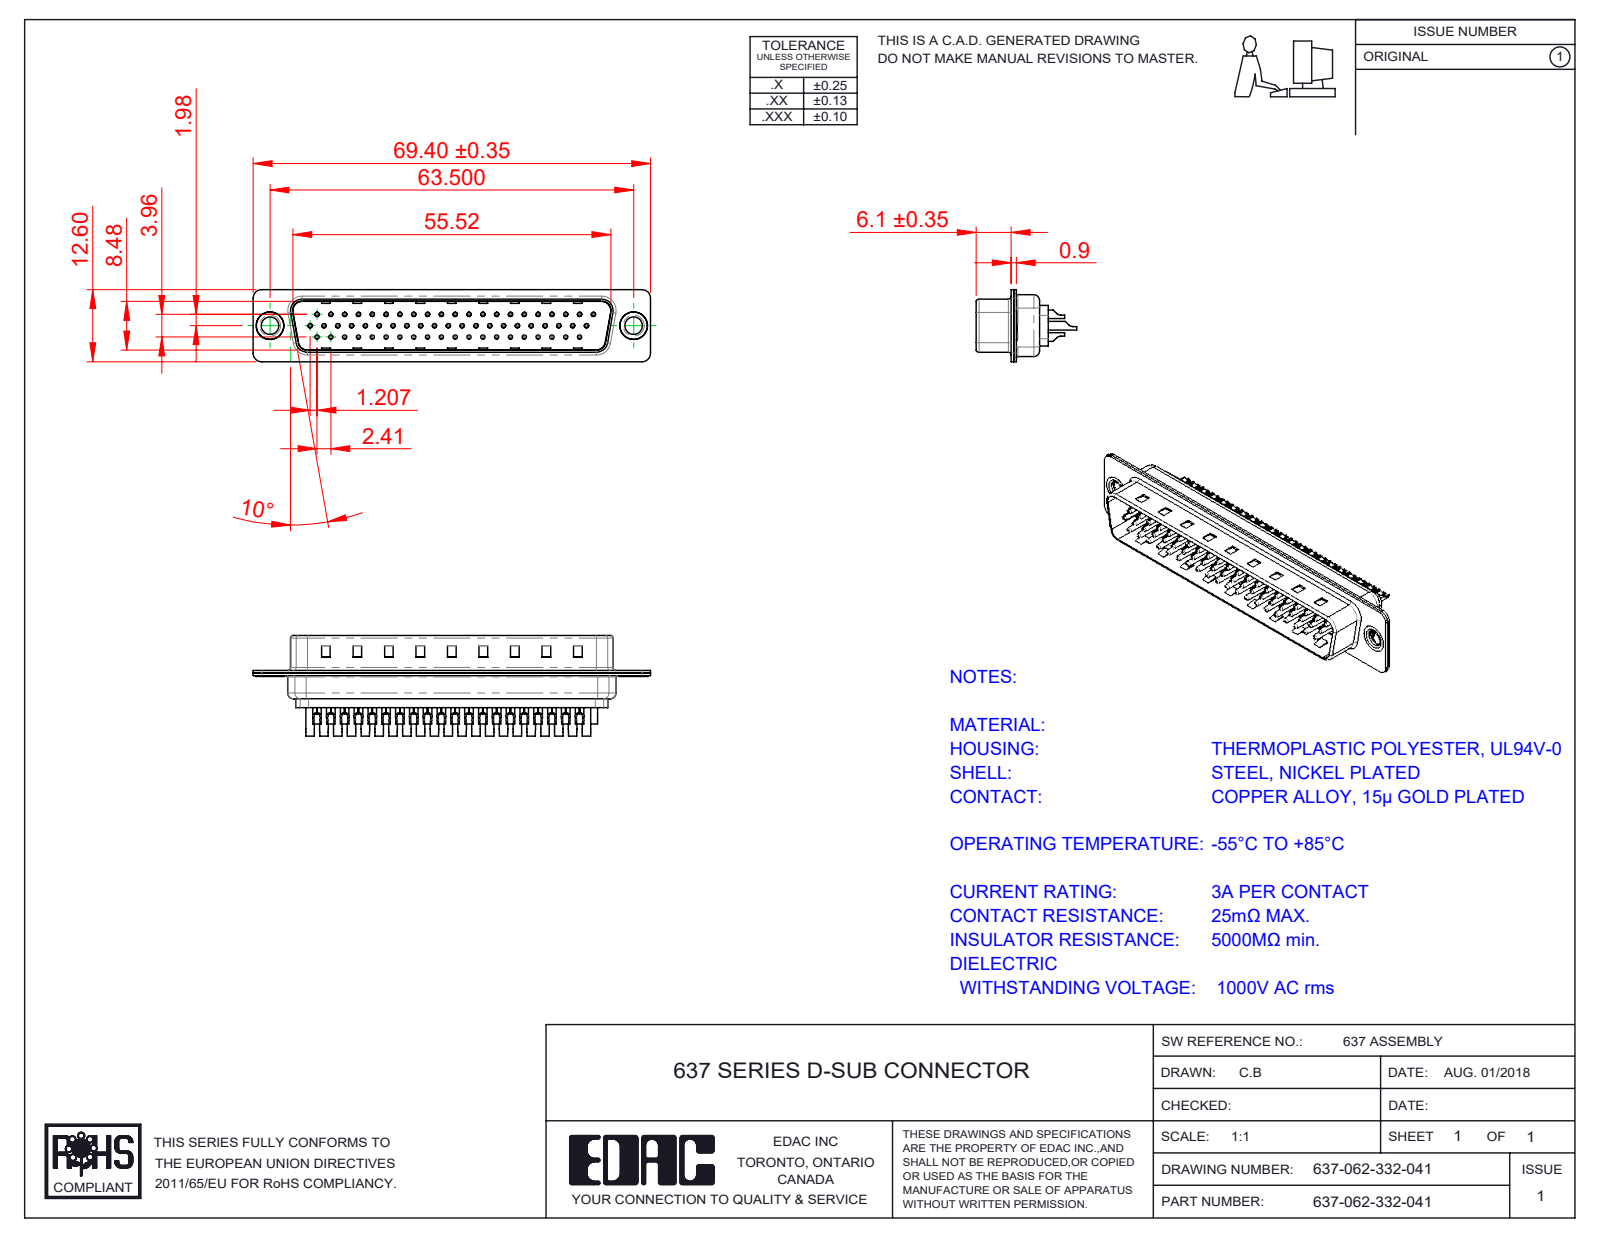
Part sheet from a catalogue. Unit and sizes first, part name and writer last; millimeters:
Units: millimetres
Overall size (bounding box): 69.4 × 17.55 × 12.6
Round holes (diameter × count): ⌀0.35 ×62, ⌀1.1 ×62, ⌀1.6 ×62, ⌀3.05 ×2, ⌀4 ×2, ⌀4.8 ×2
Round bosses / shafts (diameter × count): ⌀2 ×62, ⌀1.5 ×62, ⌀0.75 ×62, ⌀5 ×2, ⌀4.9 ×2, ⌀3.55 ×2
Partial cylindrical surfaces — rounded edges, fillets, slot ends (radius × count): R1.5 ×16, R2 ×12, R0.5 ×8, R1 ×7, R0.25 ×4, R0.55 ×4, R0.7 ×4, R0.95 ×4
Main face-to-face distances: 0.45, 0.4, 0.7, 8.88, 8.48, 0.9, 9.64, 0.31, 0.76, 1.16
Hole centre spacings: 7.24, 2.32, 2.41, 4.13, 9.65, 4.83, 14.48, 11.04
Volume: 3 672 mm³ · Surface area: 14 026 mm²
Bodies: 67 solids, 4354 faces (1071 planar, 1923 cylindrical, 1360 other)
Part name (STEP PRODUCT): 637 Shell Front_62 Contacts; 637 Thru Hole Rivet; 637 Shell Rear_62 Contacts; 637 Contact Row 3_32 (+4 more)
STEP written by: SolidWorks 2020 (CONFIG_CONTROL_DESIGN)
